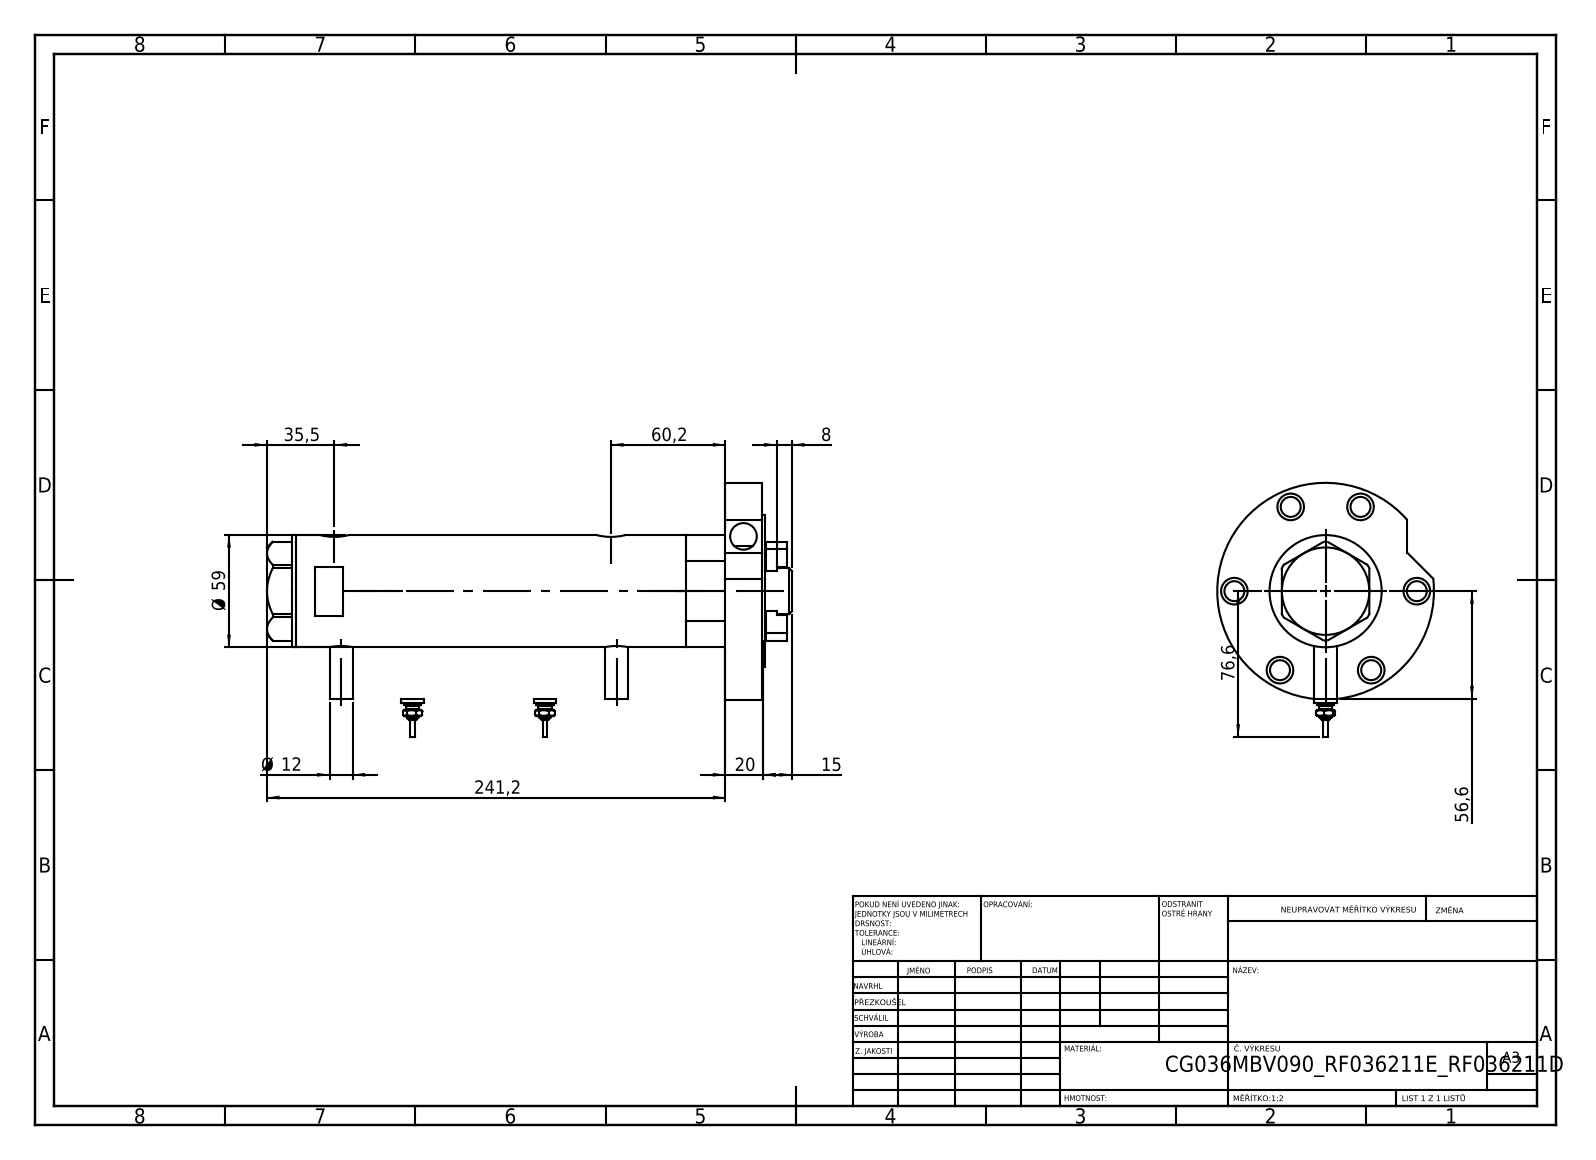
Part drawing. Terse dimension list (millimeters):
name: V270CG_VC; V270CG_RF211E; V270CG_RF211D; V270CG_BACK (+3 more)
written by: SolidWorks 2019 (CONFIG_CONTROL_DESIGN)
unit: mm
bodies: 9 solids, 296 faces (114 planar, 118 cylindrical, 64 other)
size: 276.2 × 133.6 × 114
volume: 782 533 mm³; area: 165 775 mm²
holes: 10× ⌀10.5, 7× ⌀14, 4× ⌀6.1, 2× ⌀9.73, 2× ⌀12.5, 2× ⌀15, 1× ⌀8.5, 1× ⌀25, 1× ⌀26.5, 1× ⌀36, 1× ⌀40, 1× ⌀48
bosses: 4× ⌀12, 2× ⌀9, 2× ⌀7, 2× ⌀4.5, 2× ⌀2.5, 1× ⌀114, 1× ⌀80, 1× ⌀59
face distances: 2, 19, 21, 247.2, 226.2, 245.2, 167.2, 59, 78, 80
hole spacings: 48, 19.92, 46.09, 57.24, 12, 28.22, 28.88, 35.17
